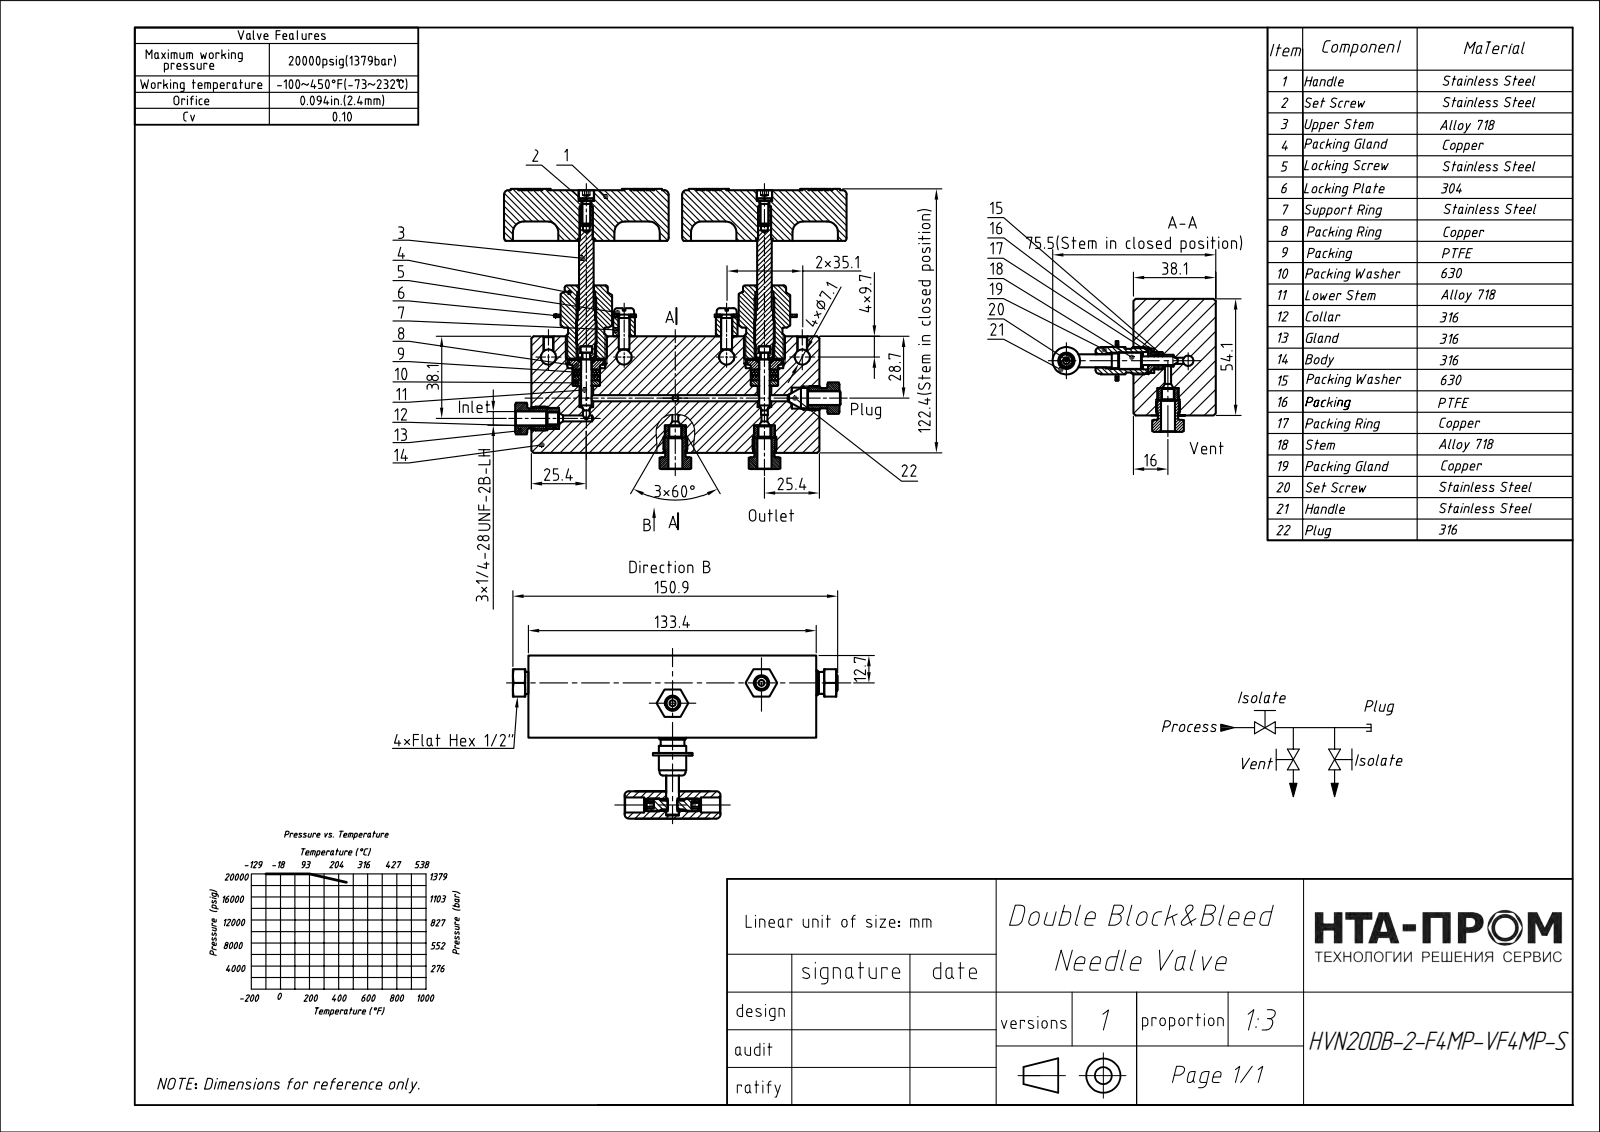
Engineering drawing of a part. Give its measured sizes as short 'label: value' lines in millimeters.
name: HVN20DB-2-F4MP-VF4MP-S; 001; 002; 003 (+6 more)
written by: FreeCAD (AUTOMOTIVE_DESIGN)
unit: mm
bodies: 18 solids, 1172 faces (290 planar, 387 cylindrical, 495 other)
size: 158.8 × 131.14 × 75.61
volume: 336 766 mm³; area: 64 851 mm²
holes: 4× ⌀5.49, 4× ⌀6.49, 4× ⌀7.1, 2× ⌀5, 2× ⌀5.98, 2× ⌀7, 2× ⌀8.26, 1× ⌀6.17
bosses: 4× ⌀11.1, 4× ⌀9.59, 4× ⌀9.4, 2× ⌀15.4, 2× ⌀14, 2× ⌀10.87, 2× ⌀10, 2× ⌀7.5
rounds: 57× R0.3, 41× R0.75, 24× R2, 8× R25.43, 4× R3, 4× R7.33, 3× R7.5, 2× R11
face distances: 38.1, 54.1, 133.4, 123.19, 69.09, 99.69, 45.59, 23.5, 10.08, 15.6
hole spacings: 82.6, 15.75, 29.31, 30.41, 35.1, 42.36, 61.84, 67.49
